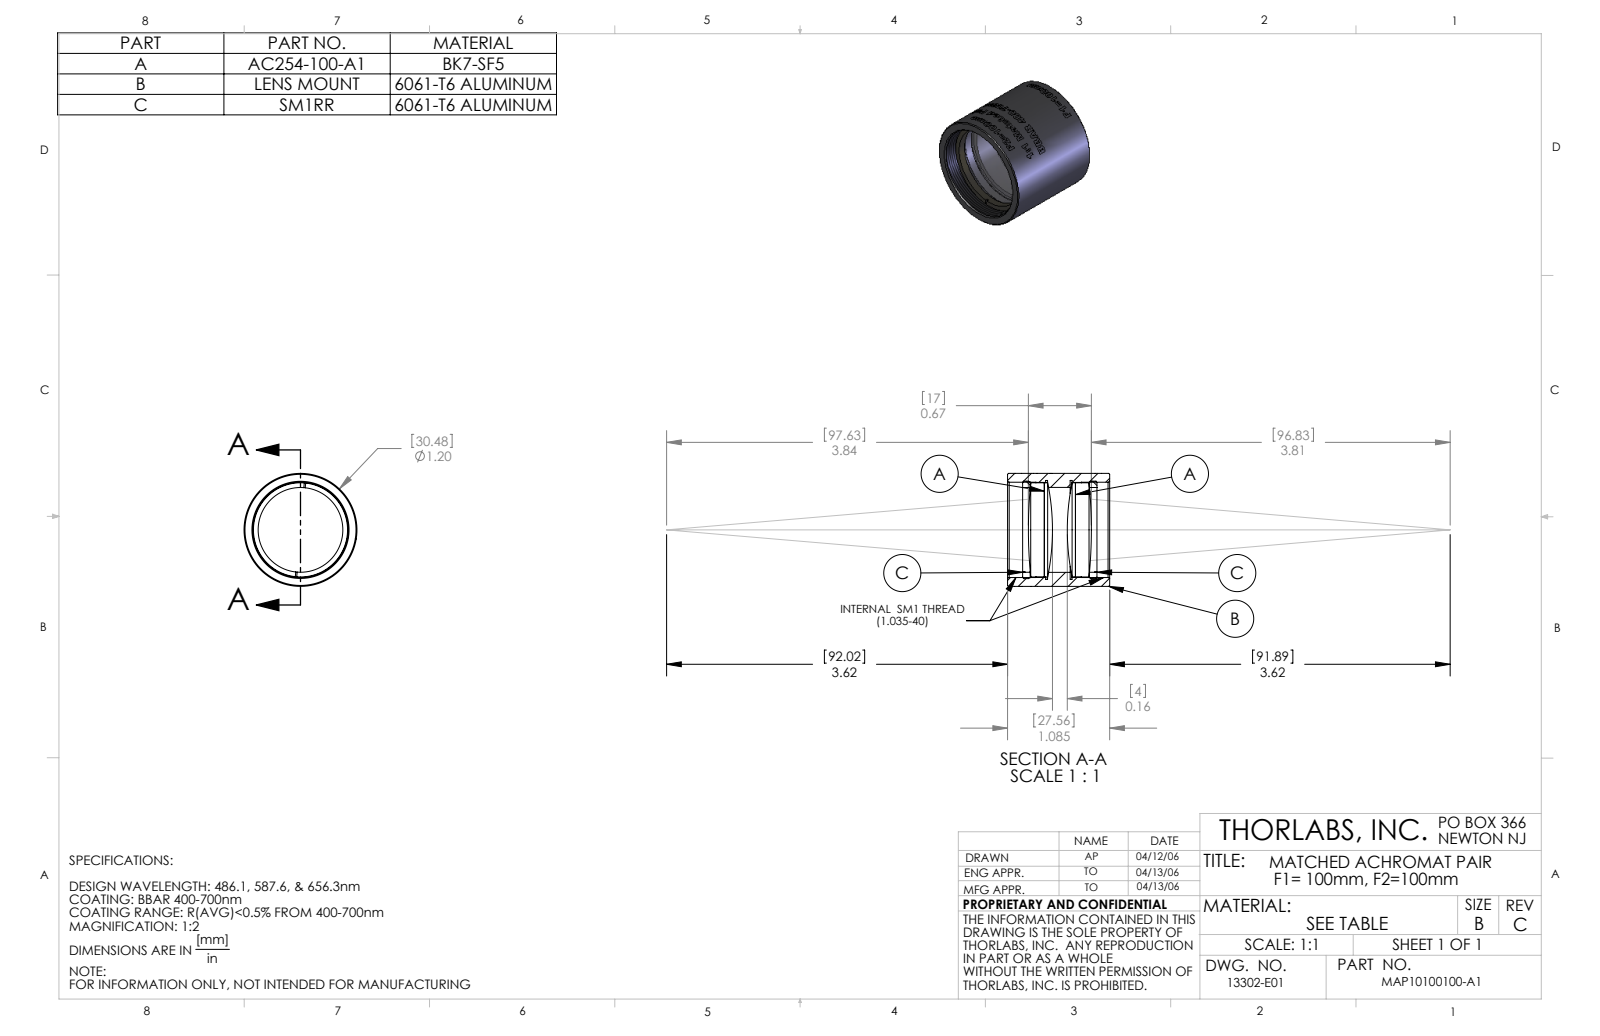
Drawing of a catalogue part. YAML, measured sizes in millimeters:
part_name: "13302-E0W"
step_written_by: "SolidWorks 2007 (AUTOMOTIVE_DESIGN)"
units: millimeters
bodies: {solids: 0, faces: 149, planar: 18, cylindrical: 115, other: 16}
overall_size: [30.48, 30.48, 27.56]
round_holes:
  - {diameter: 22.86, count: 1}
  - {diameter: 25.7, count: 1}
round_bosses_or_shafts:
  - {diameter: 30.48, count: 1}
face_to_face_distances: [27.56, 4.07, 23.49, 3.43, 20.06, 24.13, 0.38, 0.64, 19.42, 22.85]
